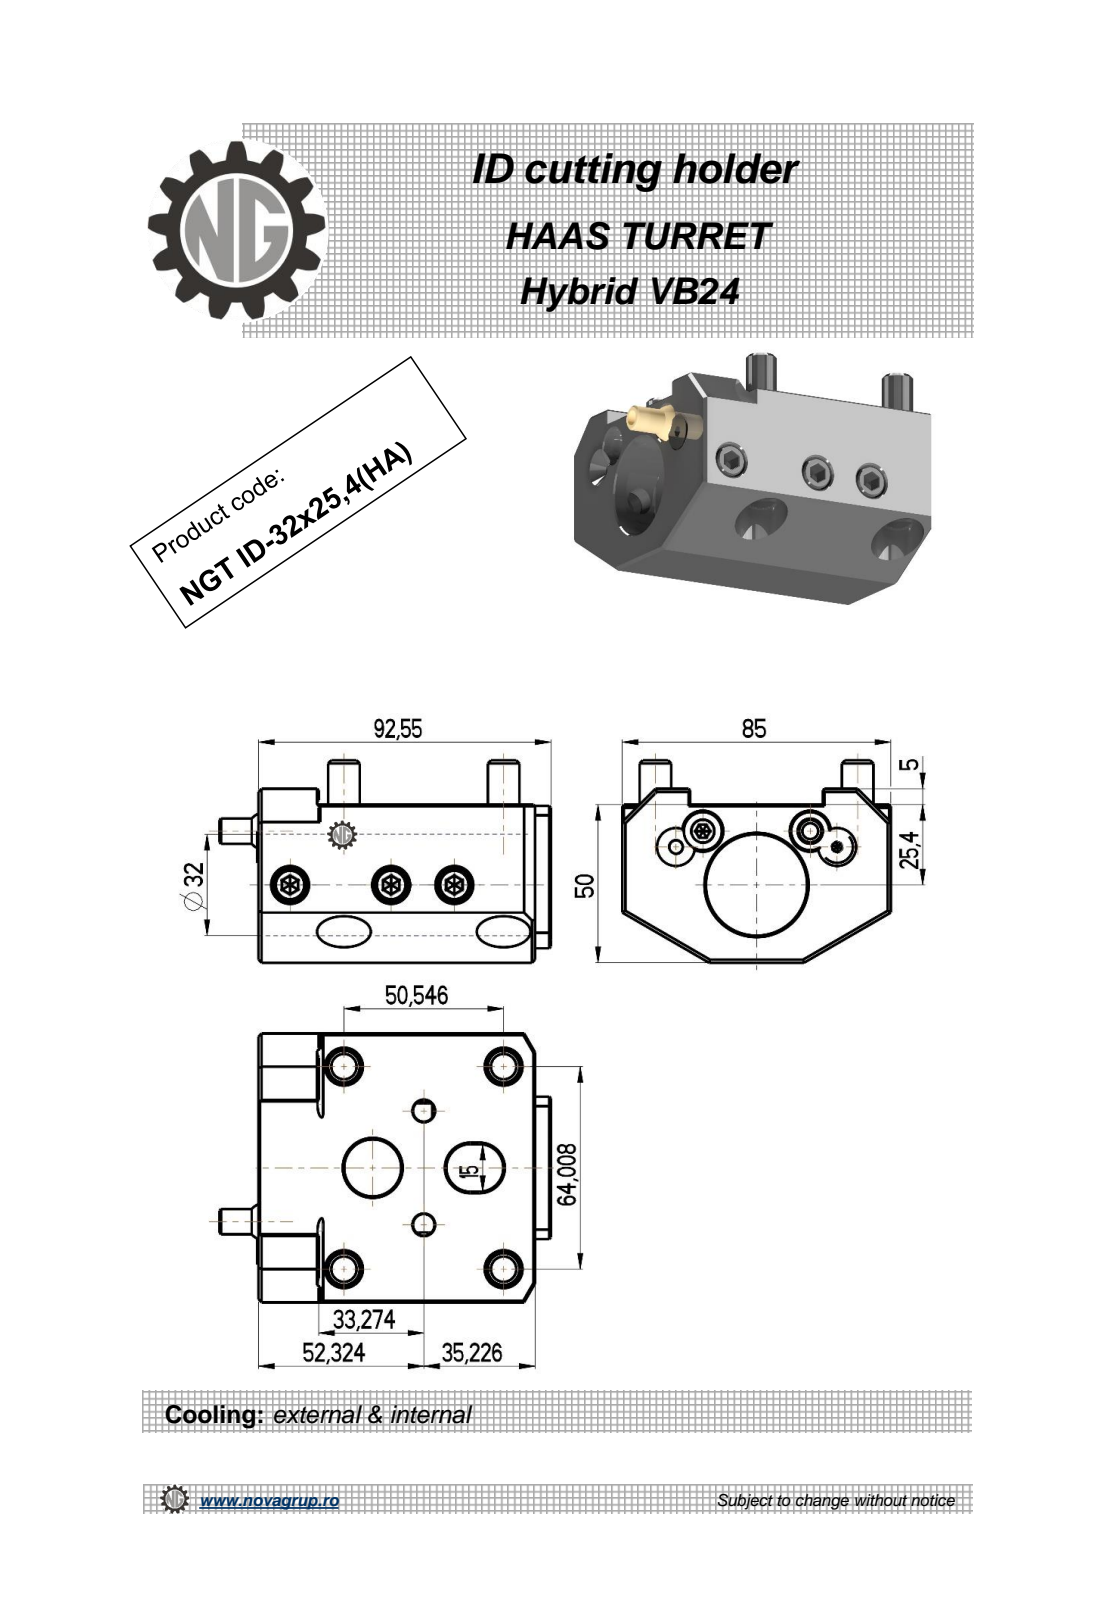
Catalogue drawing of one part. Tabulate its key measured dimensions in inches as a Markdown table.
| quantity | value |
| --- | --- |
| part name | NGT_ID_32_25_4_HA |
| STEP written by | PRO/ENGINEER BY PARAMETRIC TECHNOLOGY CORPORATION, 2010280 (CONFIG_CONTROL_DESIGN) |
| units | inches |
| bodies | 1 solid, 339 faces (137 planar, 101 cylindrical, 101 other) |
| overall size | 4.13 × 3.346 × 2.52 |
| volume | 16.63 in³ |
| surface area | 70.53 in² |
| round holes (diameter × count) | 0.335 × 3, 0.433 × 3, 0.268 × 2, 0.197 × 1, 0.709 × 1, 1.26 × 1 |
| round bosses / shafts (diameter × count) | 0.394 × 8, 0.315 × 1 |
| partial cylindrical surfaces (radius × count) | 0.02 × 36, 0.008 × 6, 0.295 × 2 |
| main face-to-face distances | 0.197, 1.969, 3.346, 3.447, 3.644, 1.772, 0.787, 2.559, 0.394, 2.165 |
| hole center spacings | 0.953, 0.787, 0.946, 1.26, 1.417, 2.047 |
